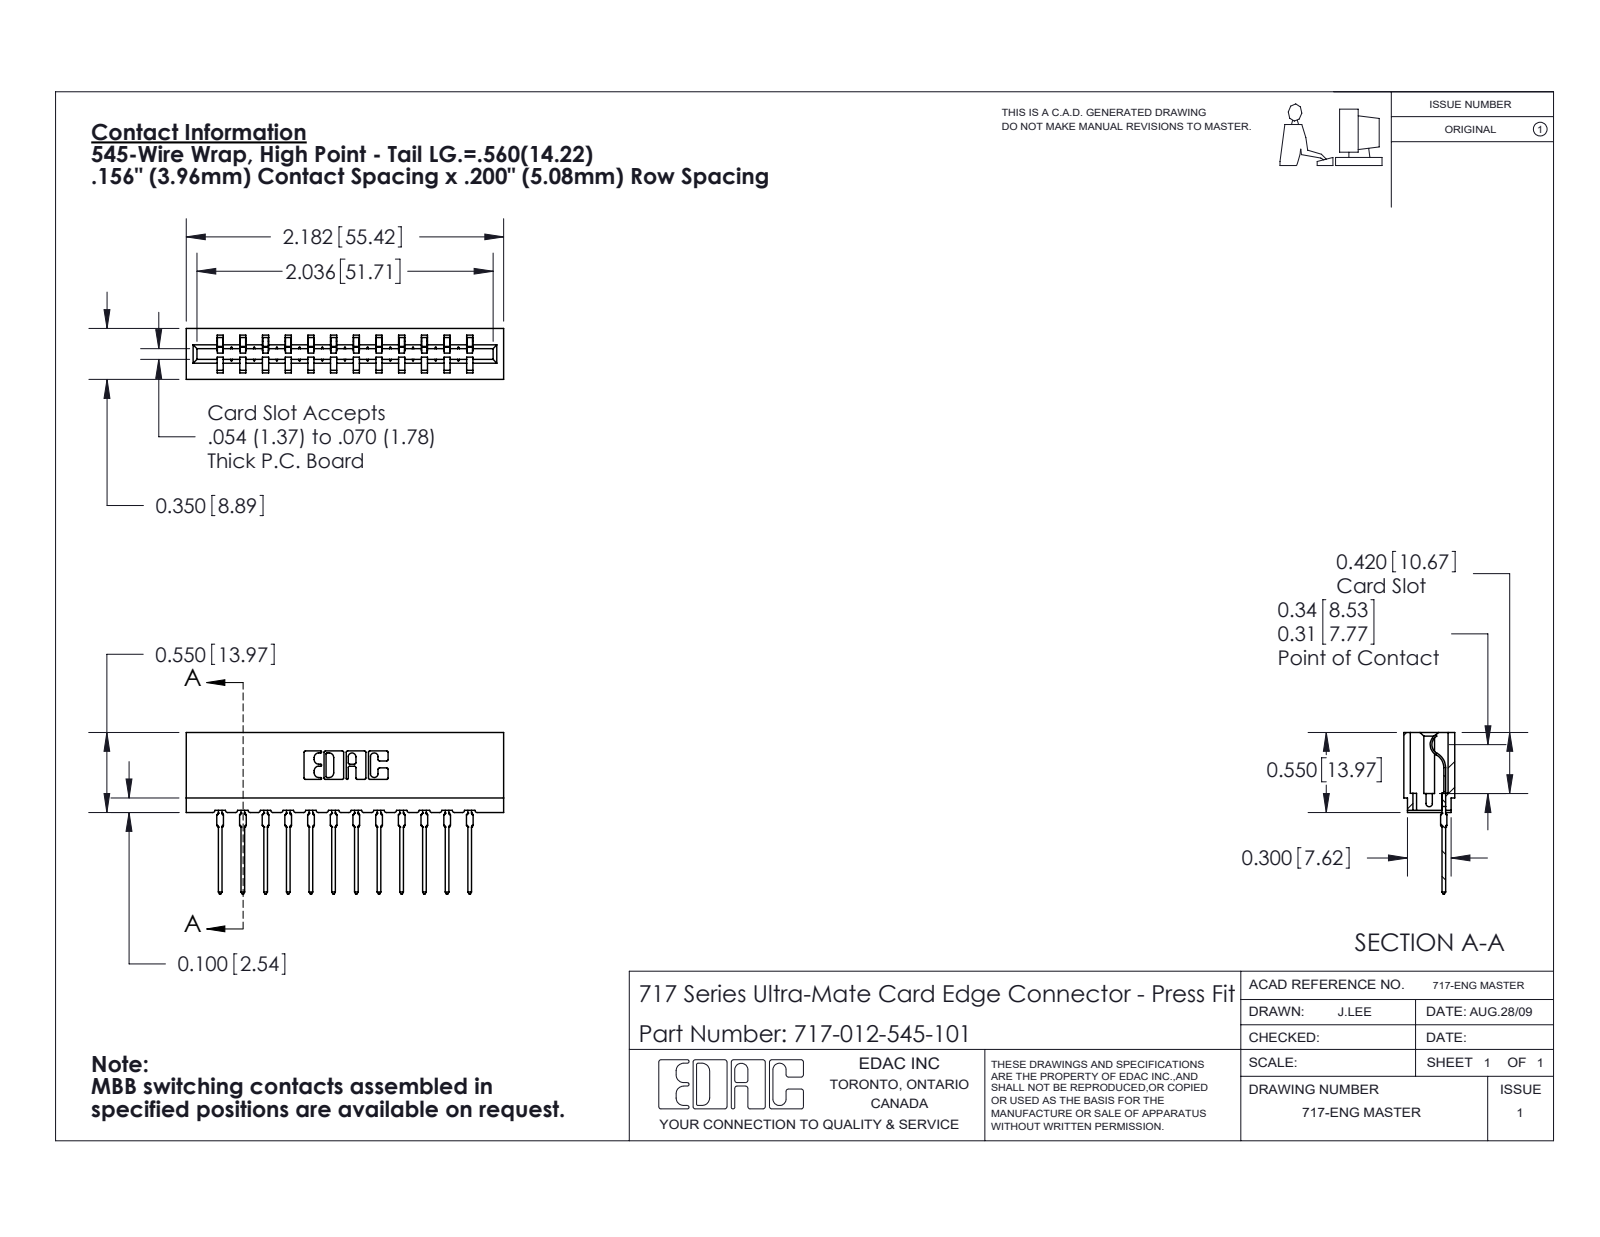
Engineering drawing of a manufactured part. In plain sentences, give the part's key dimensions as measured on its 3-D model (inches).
The part is named "745-292-001_545; 717-012-545-101; 717 Part_Insulator Option - 06". Its 3-D file was written by "SolidWorks 2020 (CONFIG_CONTROL_DESIGN)". It is 13 solids with 1450 faces: 870 planar, 268 cylindrical and 312 other. Overall it measures 2.182 by 1.109 by 0.35 inches. Its volume is 0.296 cubic inches and its surface area 10.35 square inches. Partial cylindrical surfaces (rounded edges, fillets, slot ends): 24 of radius 0.015, 24 of radius 0.021, 22 of radius 0.01, 6 of radius 0.007, 6 of radius 0.031, 4 of radius 0.005, 4 of radius 0.011, 3 of radius 0.026. The main face-to-face distances are 0.212, 0.138, 0.156, 0.624, 0.35, 0.468, 0.198, 0.312, 0.27, 0.312.
